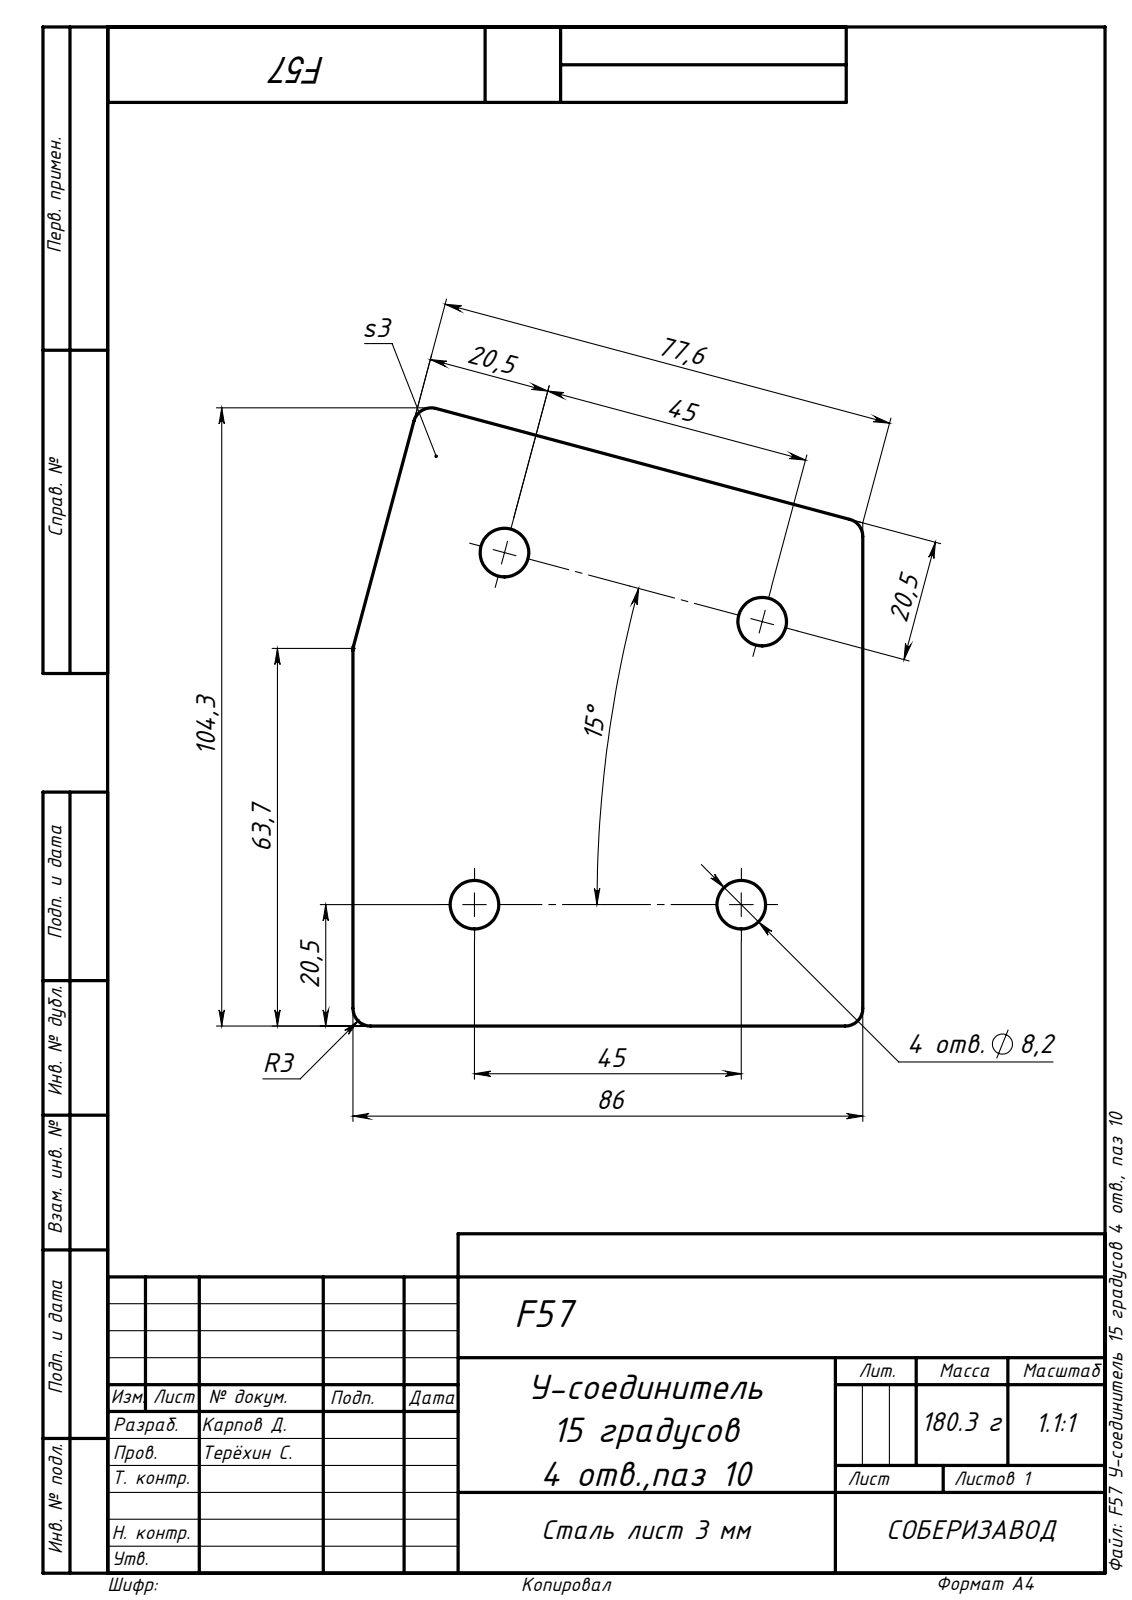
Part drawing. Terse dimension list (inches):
name: F57 У-соединитель 15 градусов 4 отв., паз 10
written by: SolidWorks 2020 (AUTOMOTIVE_DESIGN)
unit: in
bodies: 1 solid, 20 faces (7 planar, 13 cylindrical, 0 other)
size: 4.108 × 3.386 × 0.118
volume: 1.434 in³; area: 26.39 in²
holes: 4× ⌀0.323
rounds: 5× R0.118
face distances: 0.118, 3.386
hole spacings: 1.772, 1.885, 2.347, 2.681, 2.818
